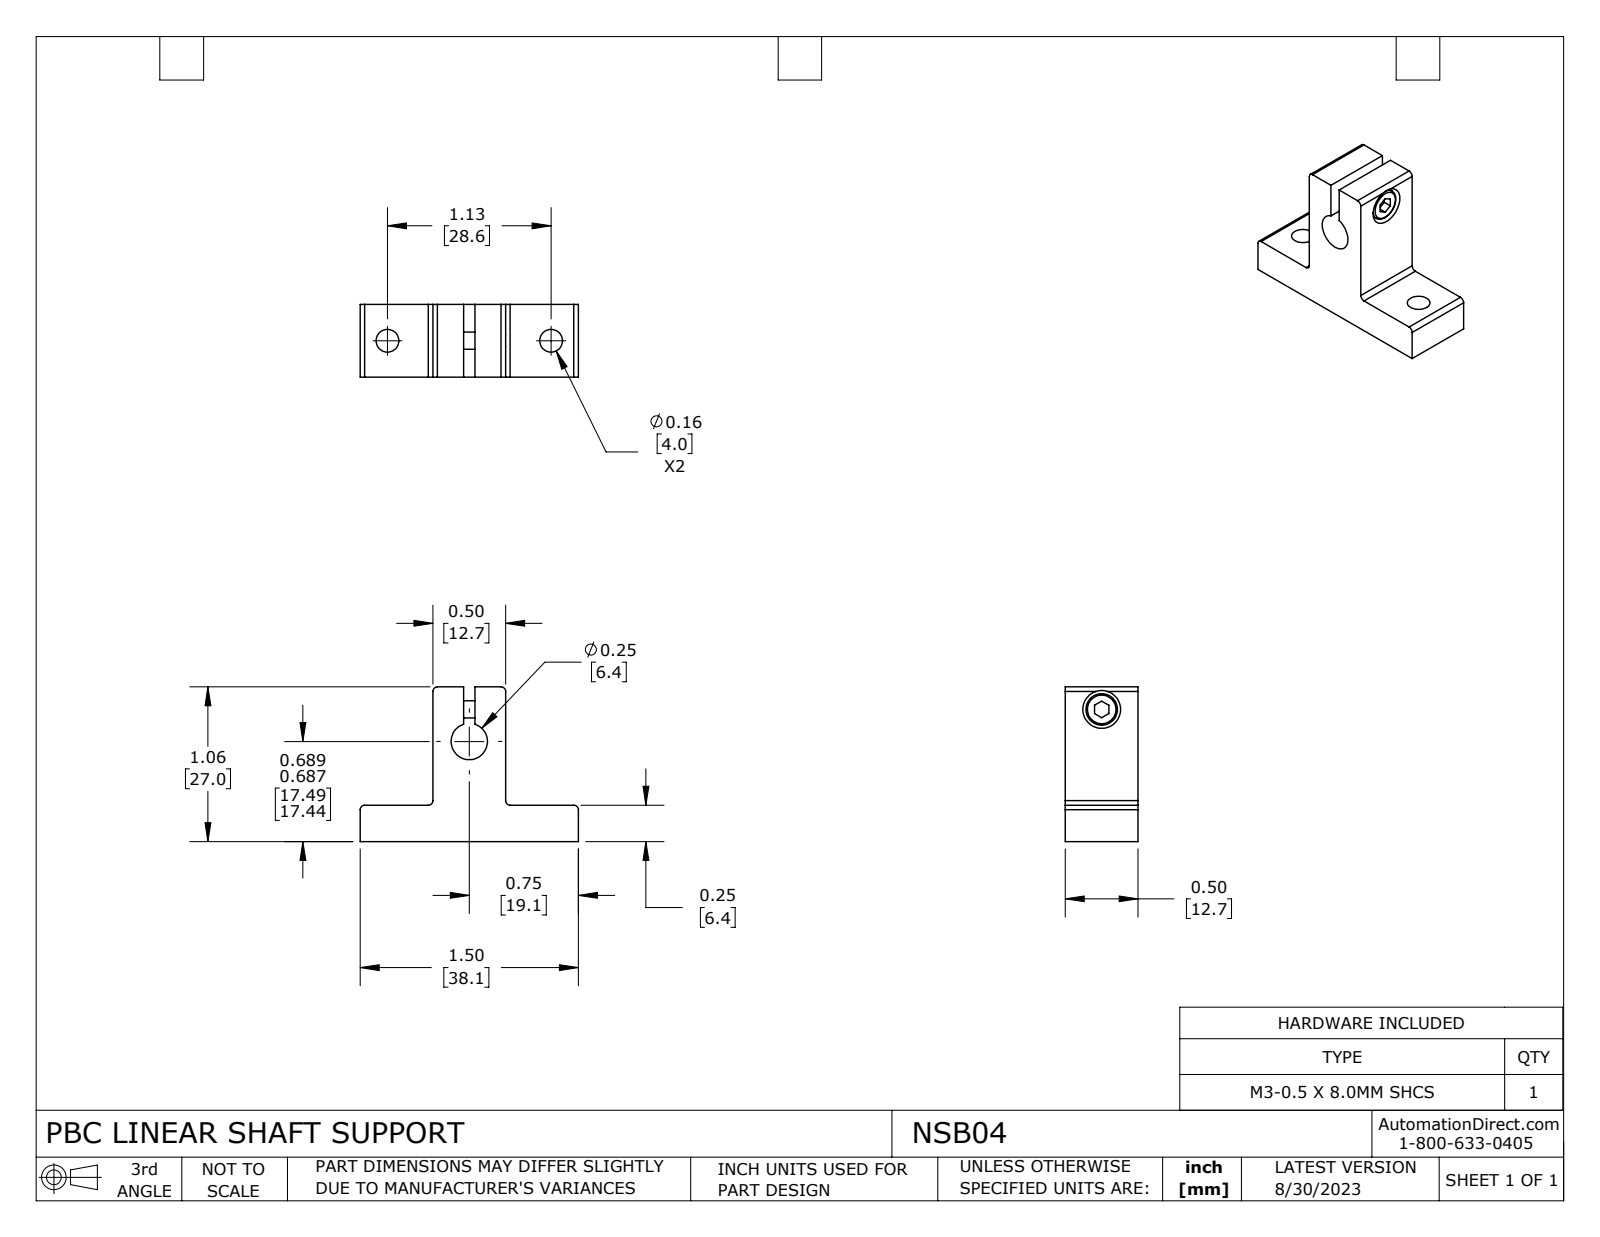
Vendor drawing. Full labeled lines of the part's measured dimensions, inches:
Part name (STEP PRODUCT): NSB04
STEP written by: SolidWorks 2023 (CONFIG_CONTROL_DESIGN)
Units: inches
Bodies: 2 solids, 51 faces (24 planar, 23 cylindrical, 4 other)
Overall size (bounding box): 1.5 × 1.063 × 0.5
Volume: 0.344 in³ · Surface area: 5.128 in²
Round holes (diameter × count): ⌀0.156 ×2, ⌀0.098 ×1, ⌀0.157 ×1, ⌀0.25 ×1, ⌀0.26 ×1
Round bosses / shafts (diameter × count): ⌀0.217 ×1, ⌀0.118 ×1
Partial cylindrical surfaces — rounded edges, fillets, slot ends (radius × count): R0.031 ×6
Main face-to-face distances: 0.5, 0.25, 0.211, 0.289, 1, 0.711, 0.789, 1.063, 0.813, 1.5
Hole centre spacings: 1.125
